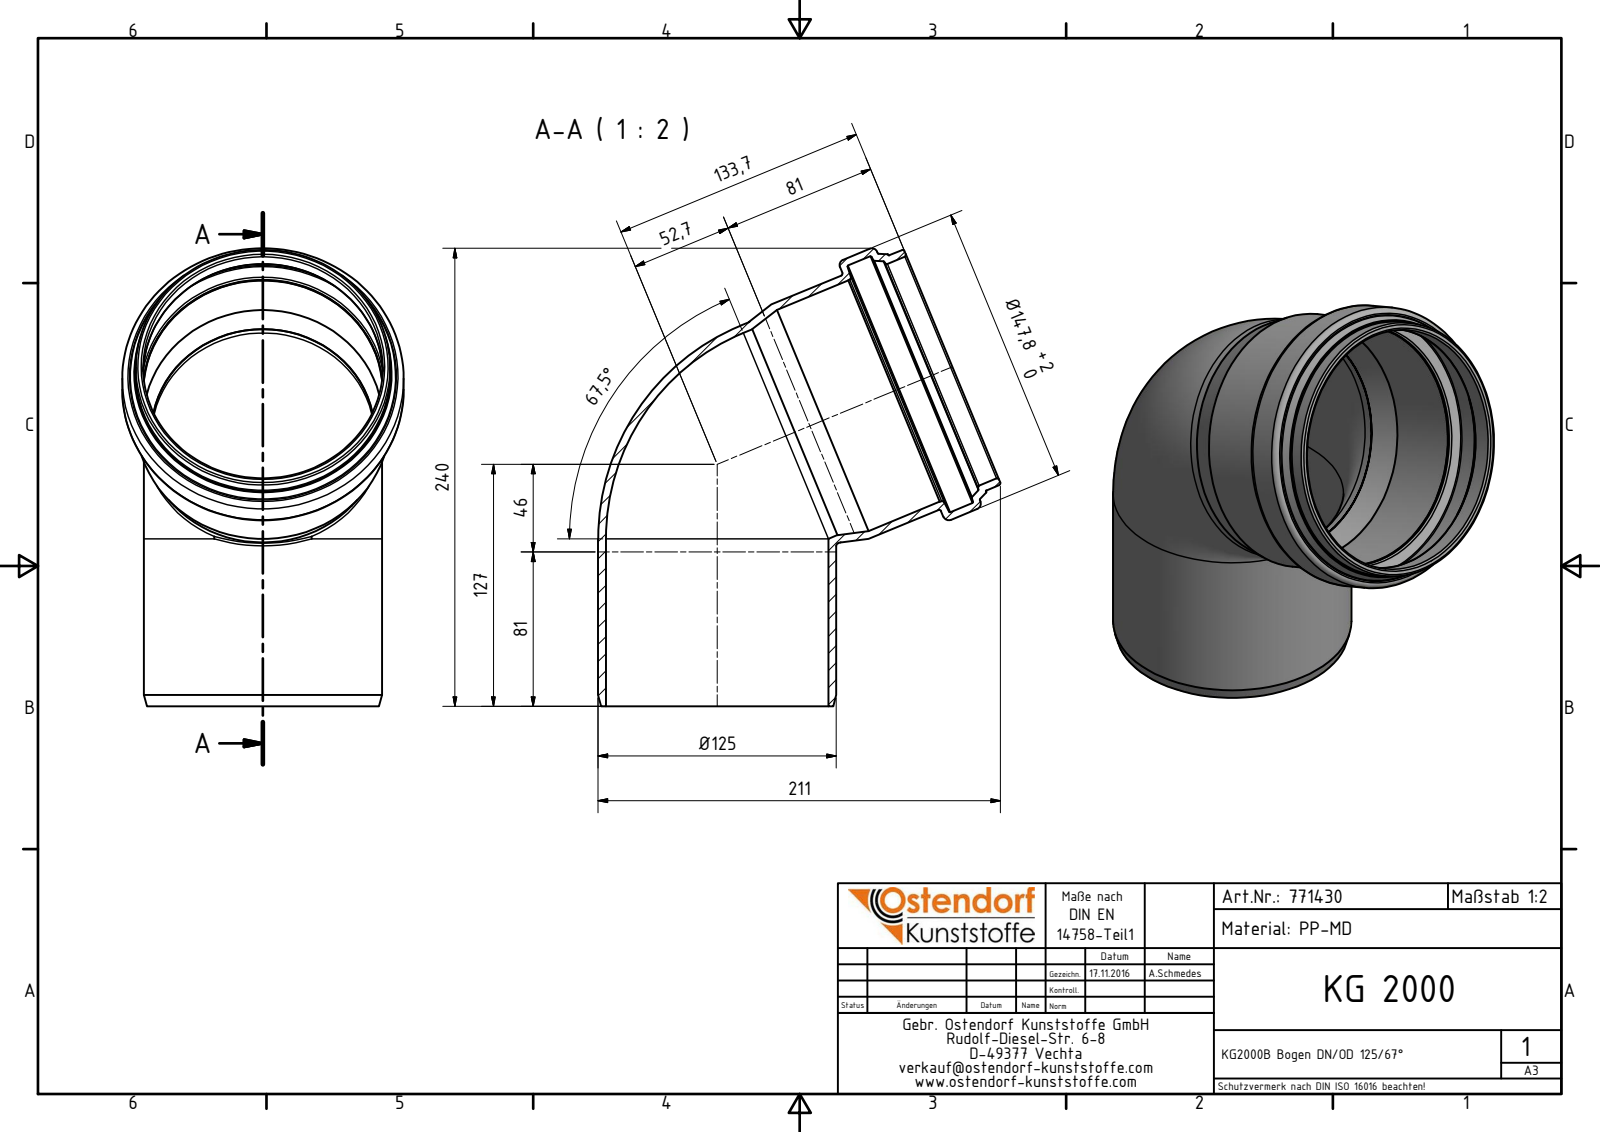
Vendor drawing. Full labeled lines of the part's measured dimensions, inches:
Part name (STEP PRODUCT): 771430 KG2000B Bogen DN_OD 125_67°
STEP written by: Autodesk Inventor 2016 (AUTOMOTIVE_DESIGN)
Units: inches
Bodies: 1 solid, 44 faces (7 planar, 11 cylindrical, 26 other)
Overall size (bounding box): 9.464 × 8.319 × 5.819
Volume: 23.22 in³ · Surface area: 323.3 in²
Round holes (diameter × count): ⌀4.602 ×2, ⌀4.957 ×2, ⌀4.945 ×1, ⌀5.52 ×1
Round bosses / shafts (diameter × count): ⌀4.925 ×2, ⌀5.819 ×1, ⌀5.256 ×1, ⌀5.244 ×1
Main face-to-face distances: 1.359, 0.831, 0.528, 0.052, 0.778, 1.306, 2.168, 2.22, 2.999, 3.527
